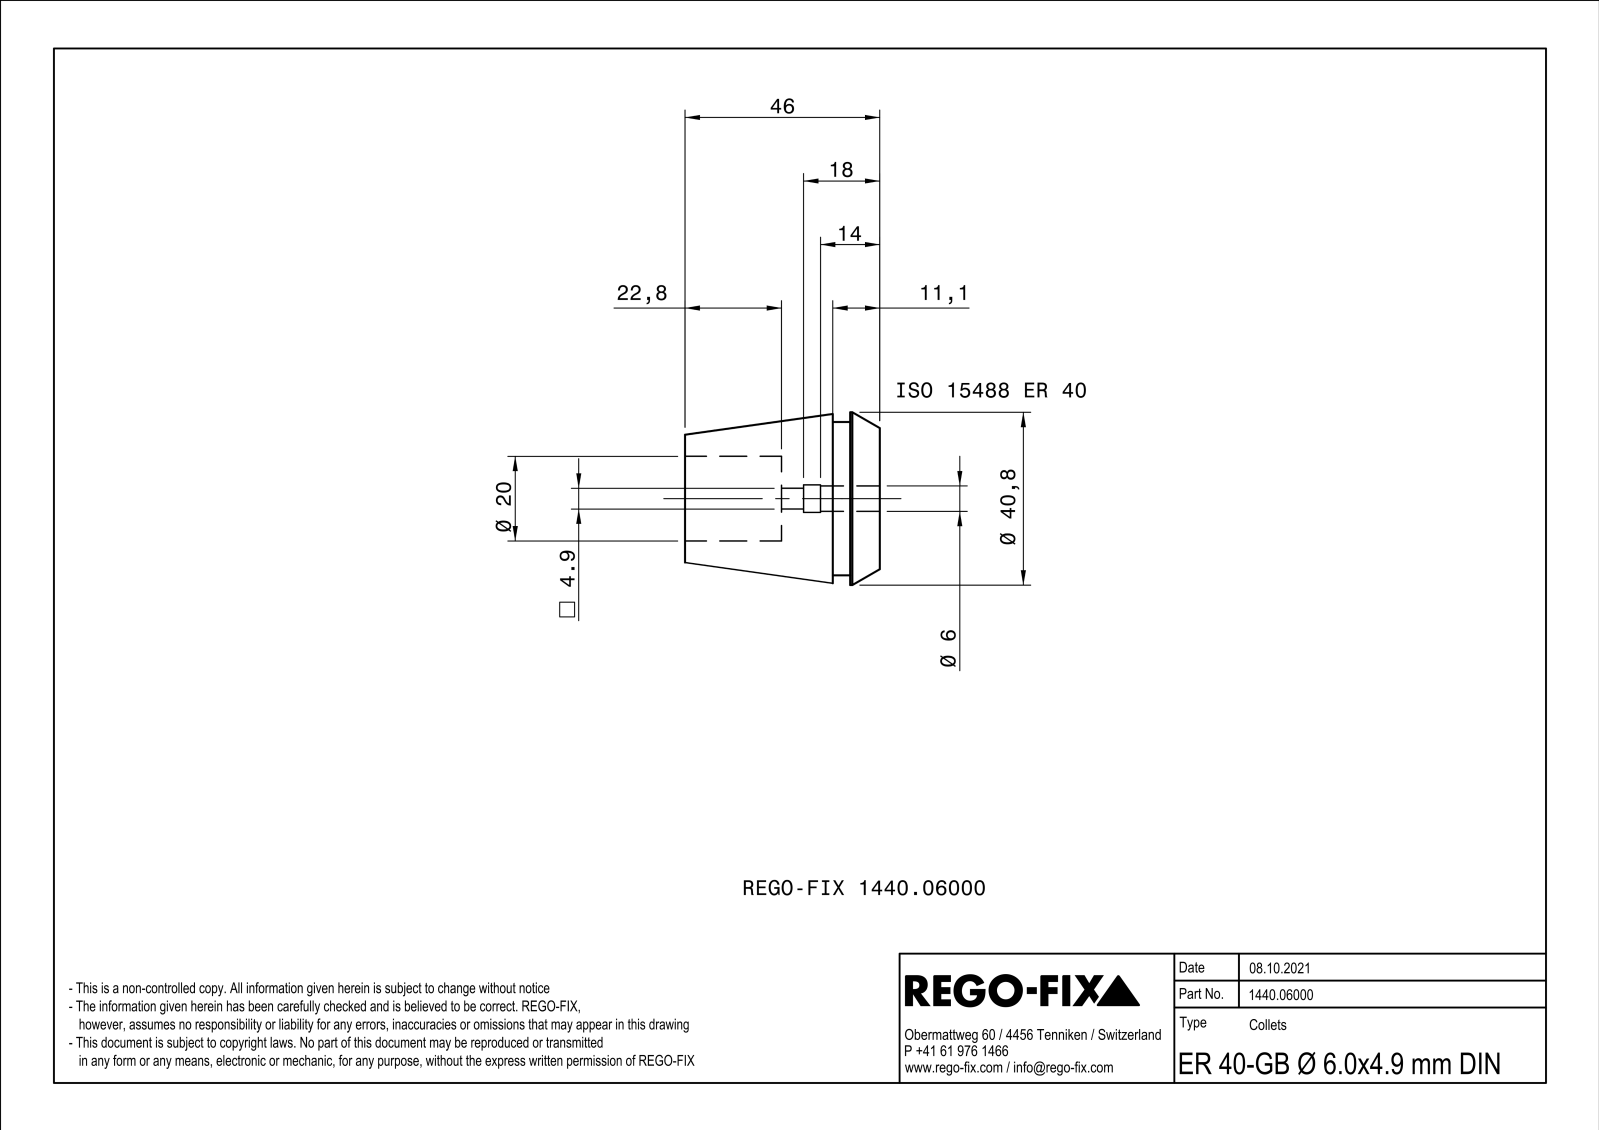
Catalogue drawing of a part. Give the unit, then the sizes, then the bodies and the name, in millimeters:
Units: millimetres
Overall size (bounding box): 46 × 40.79 × 40.79
Round holes (diameter × count): ⌀20 ×1
Round bosses / shafts (diameter × count): ⌀40.8 ×1, ⌀36.2 ×1
Partial cylindrical surfaces — rounded edges, fillets, slot ends (radius × count): R2.8 ×1, R3 ×1, R3.15 ×1, R3.25 ×1
Main face-to-face distances: 1, 46, 7, 39, 11.1, 4.1, 34.9, 23.2, 16.2, 12.1
Volume: 34 443 mm³ · Surface area: 15 663 mm²
Bodies: 1 solid, 168 faces (68 planar, 40 cylindrical, 60 other)
Part name (STEP PRODUCT): NOCUT
STEP written by: SIEMENS PLM Software Solid Edge ST10 (AUTOMOTIVE_DESIGN)
